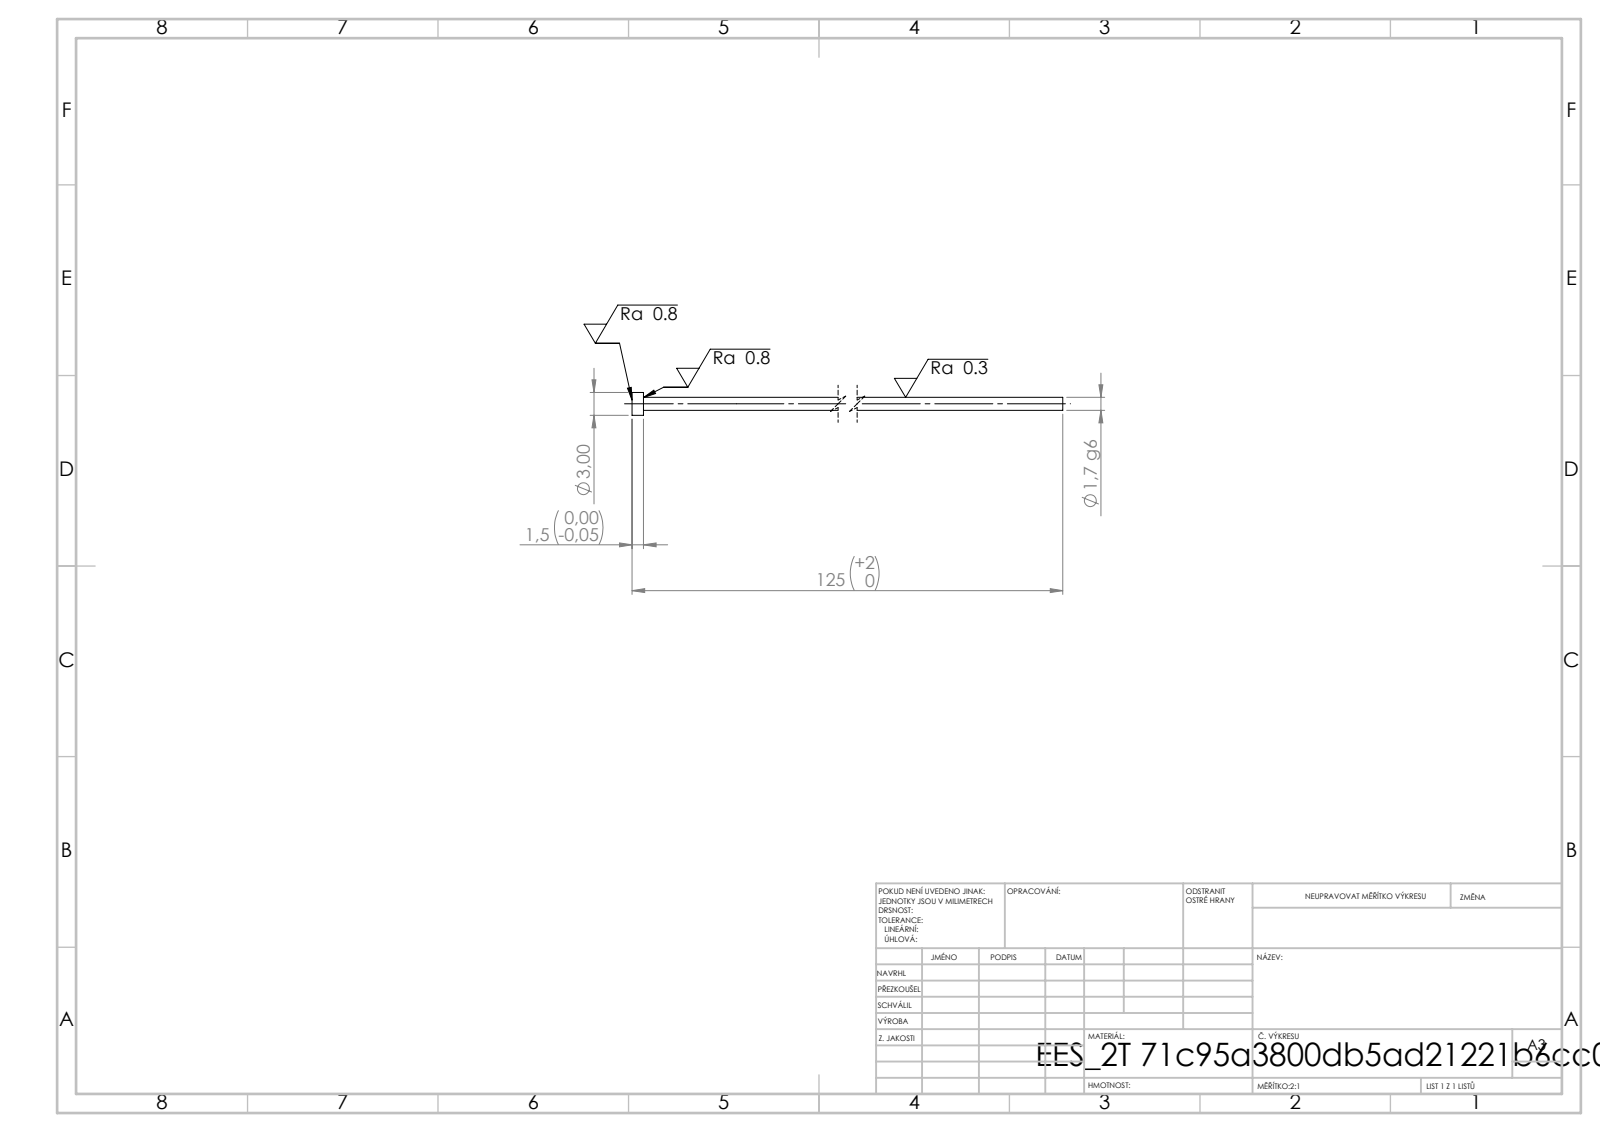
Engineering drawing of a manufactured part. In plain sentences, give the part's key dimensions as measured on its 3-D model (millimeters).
Its 3-D file was written by "SolidWorks 2019 (CONFIG_CONTROL_DESIGN)". It is 1 solid with 7 faces: 3 planar, 4 cylindrical and 0 other. Overall it measures 125 by 3 by 3 millimeters. Its volume is 291 cubic millimeters and its surface area 688 square millimeters. Round bosses or shafts: 1 of diameter 3, 1 of diameter 1.7. The main face-to-face distances are 1.5, 125, 123.5.
